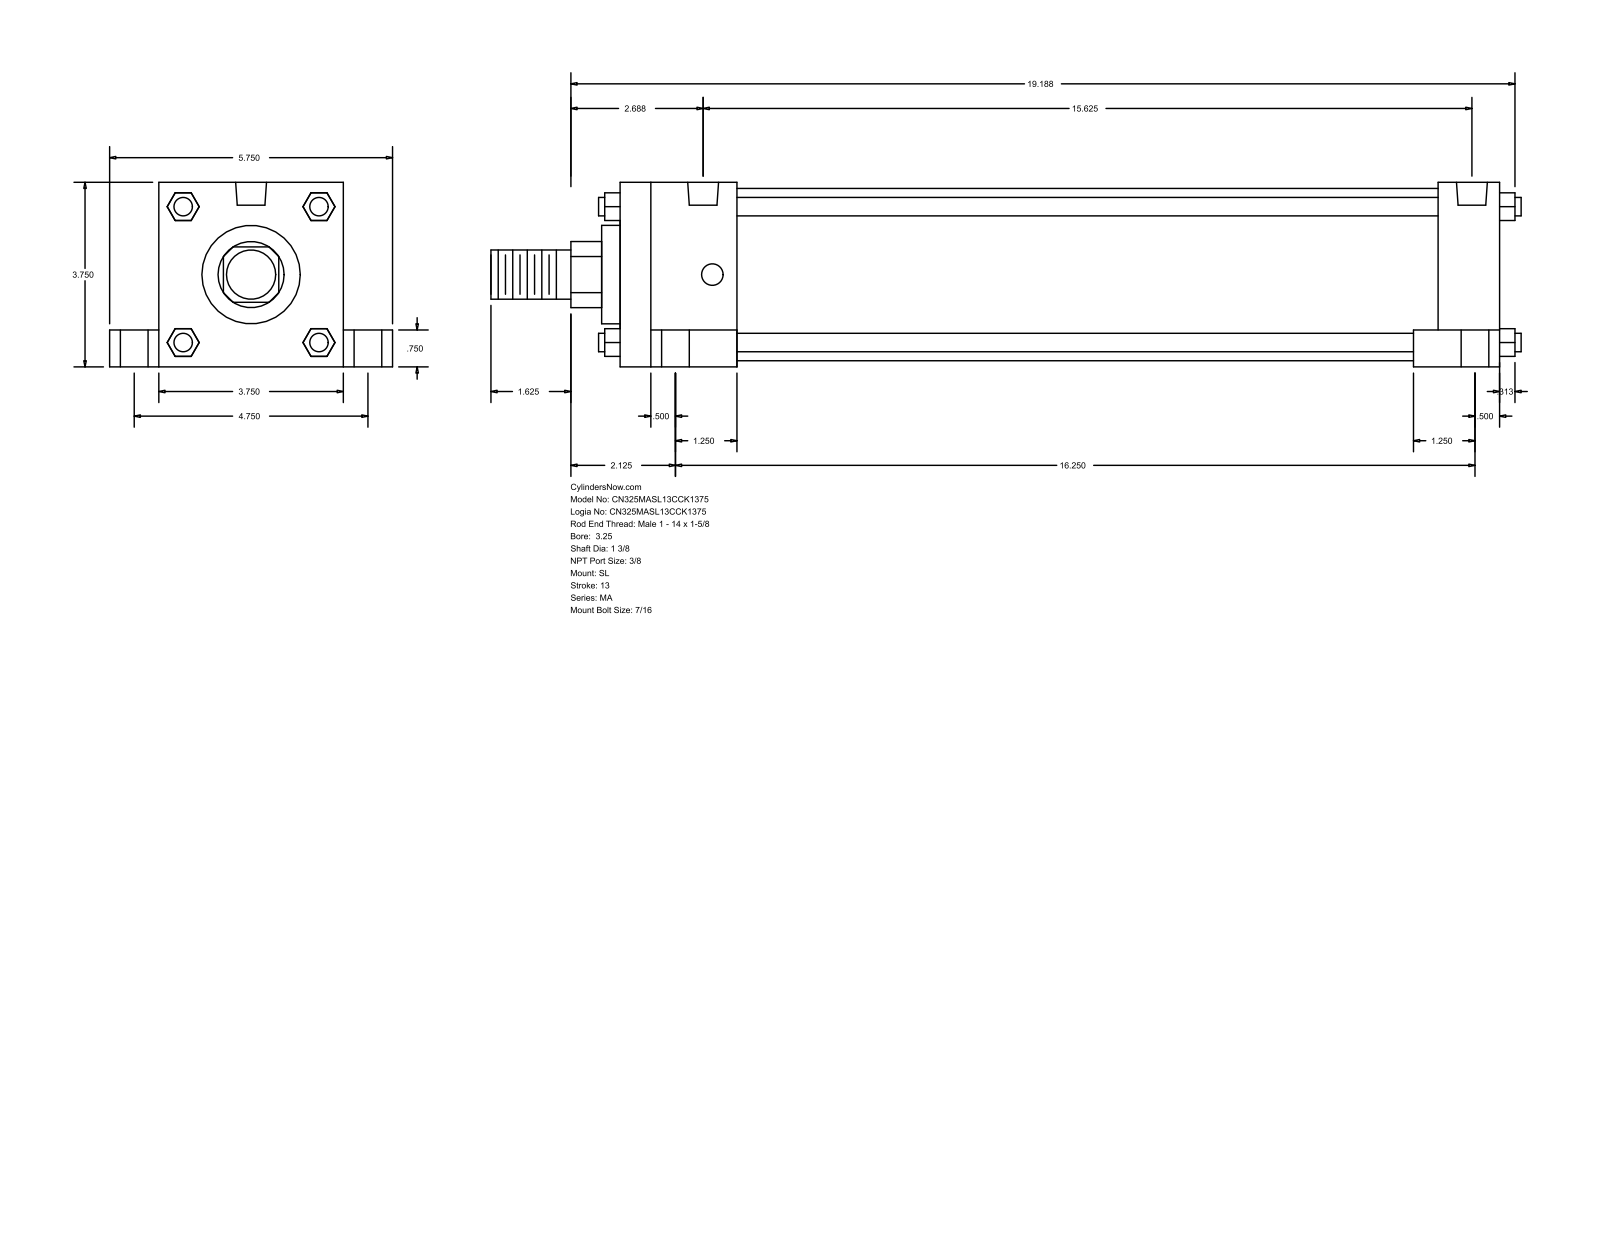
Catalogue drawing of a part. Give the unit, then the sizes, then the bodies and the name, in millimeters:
Units: millimetres
Overall size (bounding box): 531.81 × 146.05 × 95.25
Round holes (diameter × count): ⌀11.11 ×4, ⌀14.29 ×4, ⌀20.64 ×4, ⌀15.93 ×2
Round bosses / shafts (diameter × count): ⌀9.53 ×4, ⌀88.9 ×1, ⌀50.8 ×1, ⌀34.92 ×1, ⌀25.4 ×1
Partial cylindrical surfaces — rounded edges, fillets, slot ends (radius × count): R17.06 ×1
Main face-to-face distances: 95.24, 454.03, 25.41, 120.65, 422.28, 31.75, 60.32, 361.96, 393.71, 19.05
Hole centre spacings: 60.35, 60.66, 62, 63.27, 120.66, 387.35, 398.3, 403.01
Bodies: 0 solids, 148 faces (112 planar, 36 cylindrical, 0 other)
Part name (STEP PRODUCT): MA_SL__0325_1.375
STEP written by: GSSL Pune (CONFIG_CONTROL_DESIGN)
